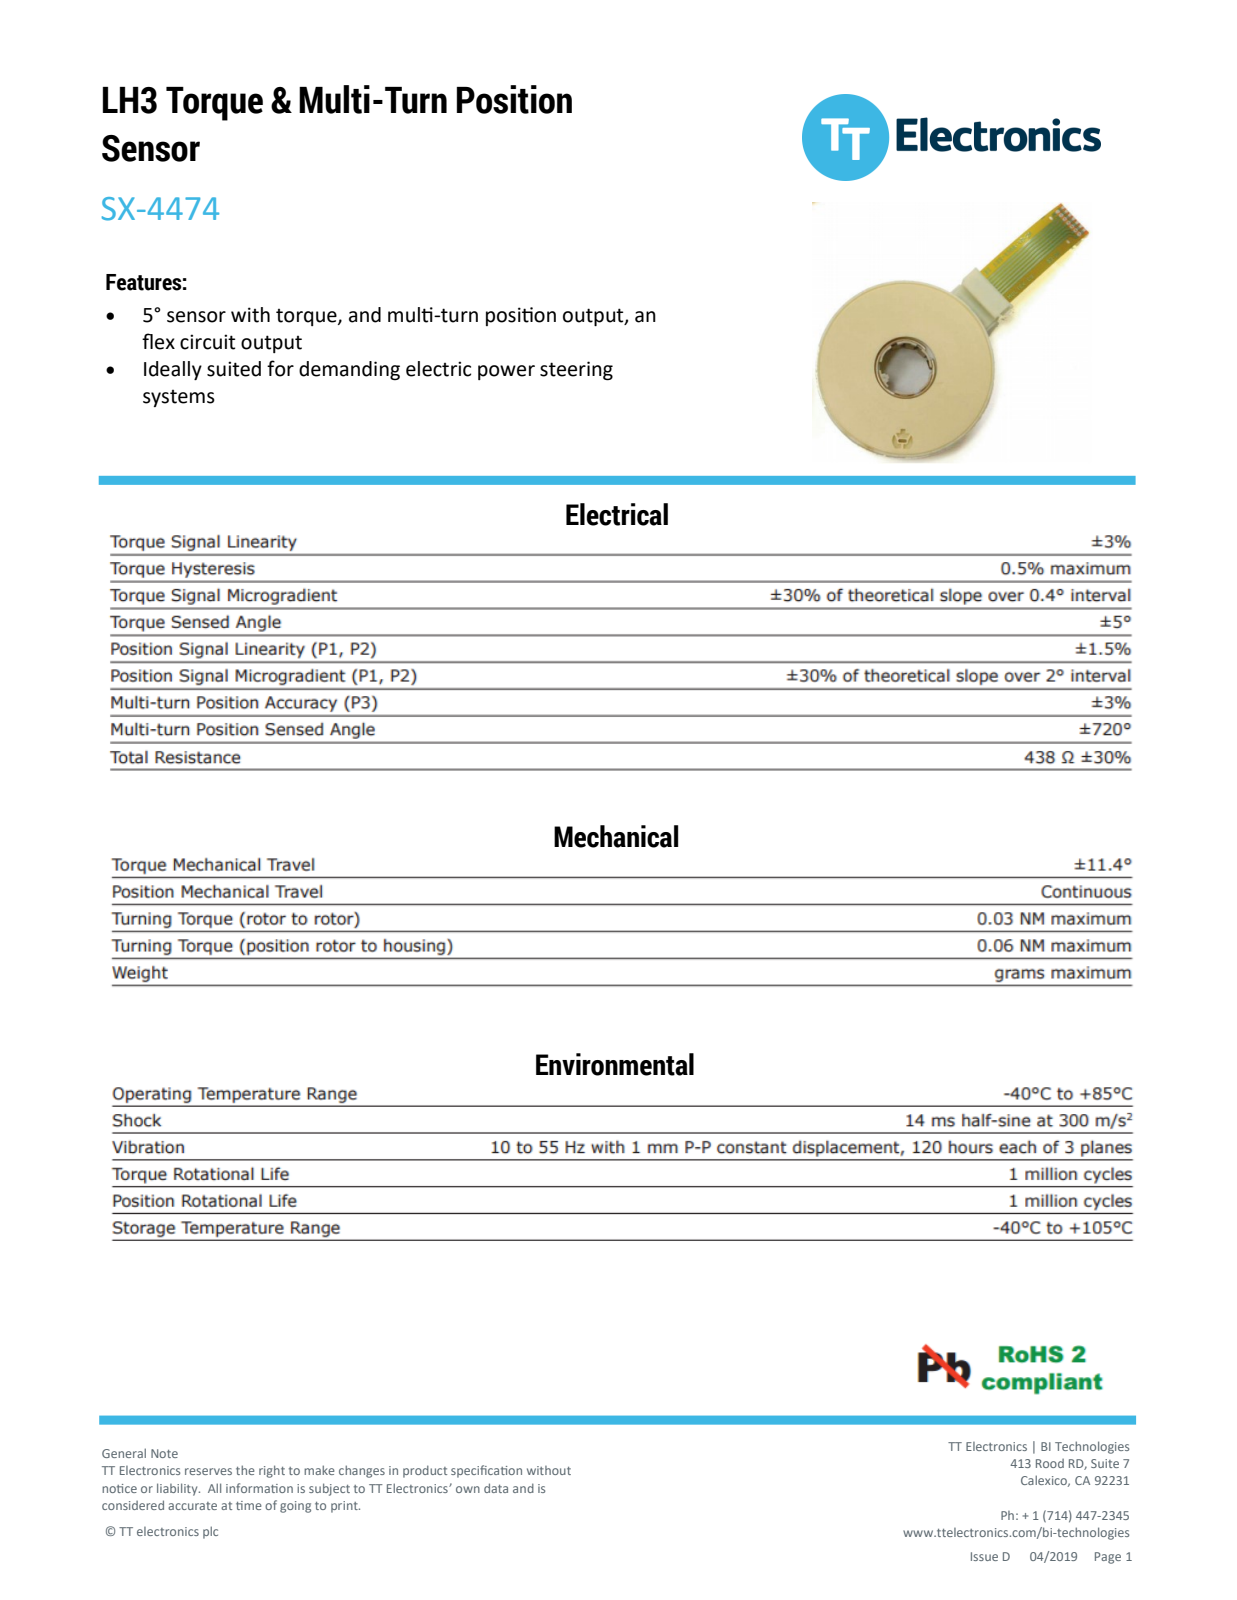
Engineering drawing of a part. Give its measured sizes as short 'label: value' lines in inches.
name: SX-4474A_SW0002
written by: CREO PARAMETRIC BY PTC INC, 2014500 (CONFIG_CONTROL_DESIGN)
unit: in
bodies: 3 solids, 2421 faces (1248 planar, 828 cylindrical, 345 other)
size: 6.283 × 3.212 × 1.728
volume: 4.854 in³; area: 73.46 in²
holes: 7× ⌀0.02, 2× ⌀0.083, 1× ⌀0.985, 1× ⌀1.046, 1× ⌀1.126, 1× ⌀1.146, 1× ⌀1.241, 1× ⌀1.247, 1× ⌀1.255, 1× ⌀2.57, 1× ⌀3.068, 1× ⌀3.09
bosses: 6× ⌀0.047, 6× ⌀0.01, 4× ⌀0.08, 1× ⌀3.142, 1× ⌀3.084, 1× ⌀3.056, 1× ⌀3.016, 1× ⌀1.345
rounds: 116× R0.01, 72× R0.007, 72× R0.012, 60× R0.006, 45× R0.005, 23× R0.02, 18× R0.016, 18× R0.028
face distances: 0.719, 0.664, 0.669, 0.05, 0.055, 0.065, 0.015, 0.661, 0.053, 0.061
hole spacings: 0.118, 0.236, 0.354, 0.472, 0.236, 0.59, 0.743, 0.746
